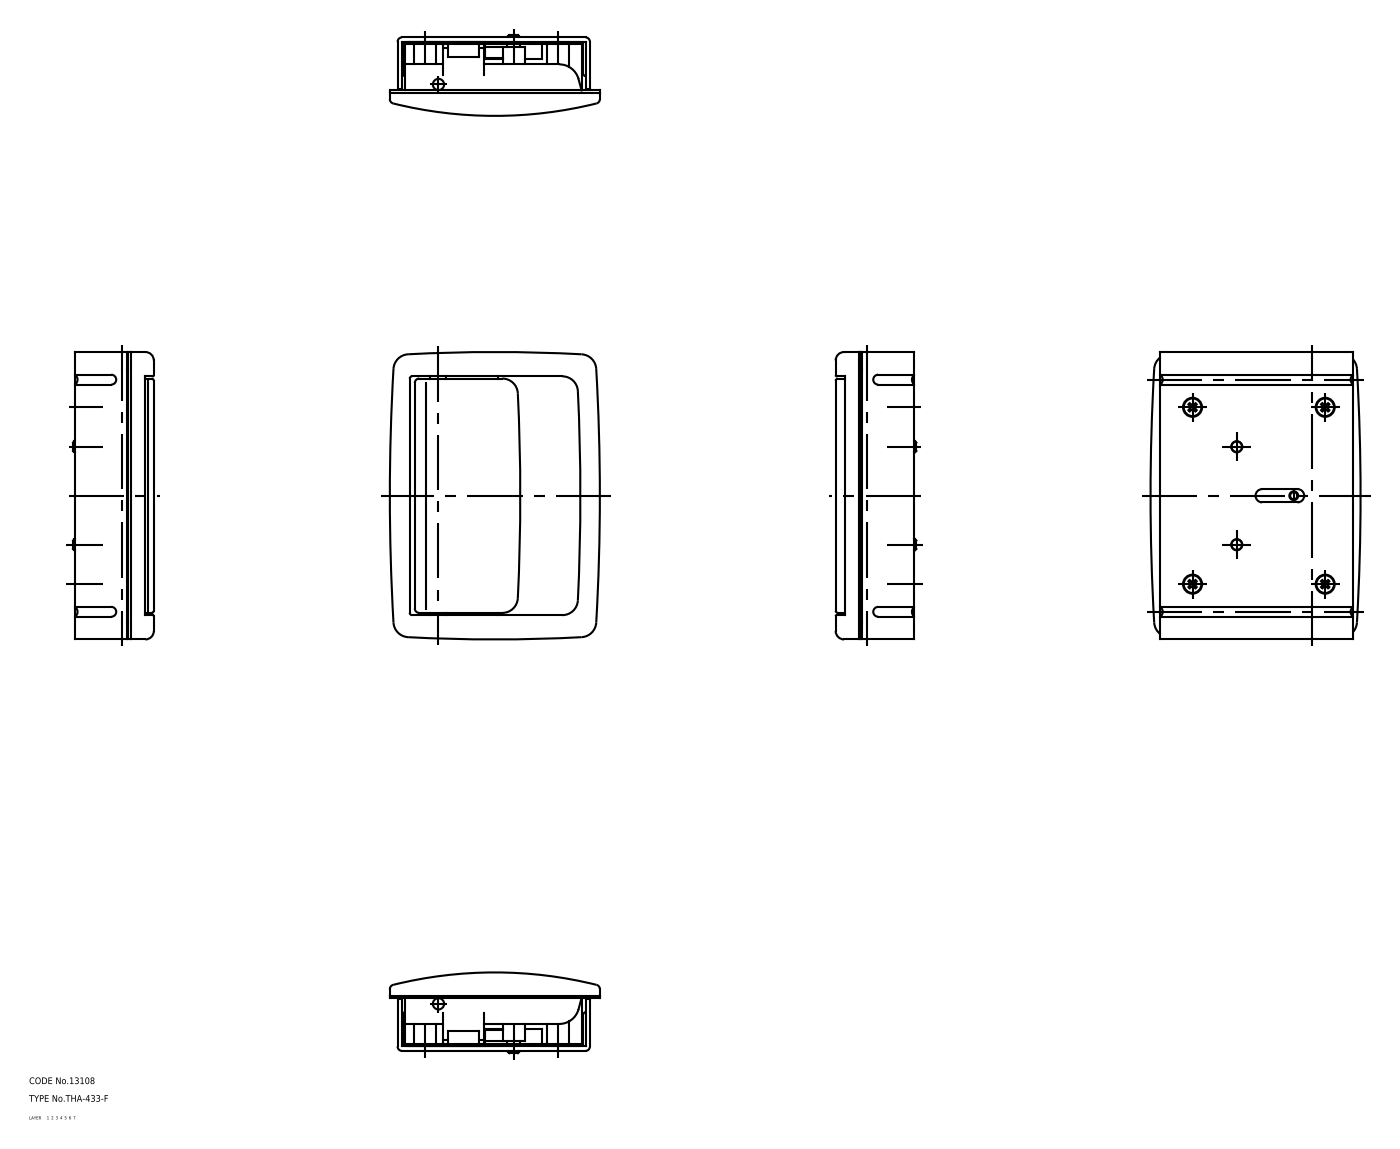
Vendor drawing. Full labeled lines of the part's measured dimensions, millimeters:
Part name (STEP PRODUCT): joint; bracket; shaft; packing (+3 more)
STEP written by: CADfix (AUTOMOTIVE_DESIGN)
Units: millimetres
Bodies: 6 solids, 476 faces (0 planar, 0 cylindrical, 476 other)
Overall size (bounding box): 130 × 95 × 36.5
Volume: 127 919 mm³ · Surface area: 103 640 mm²
